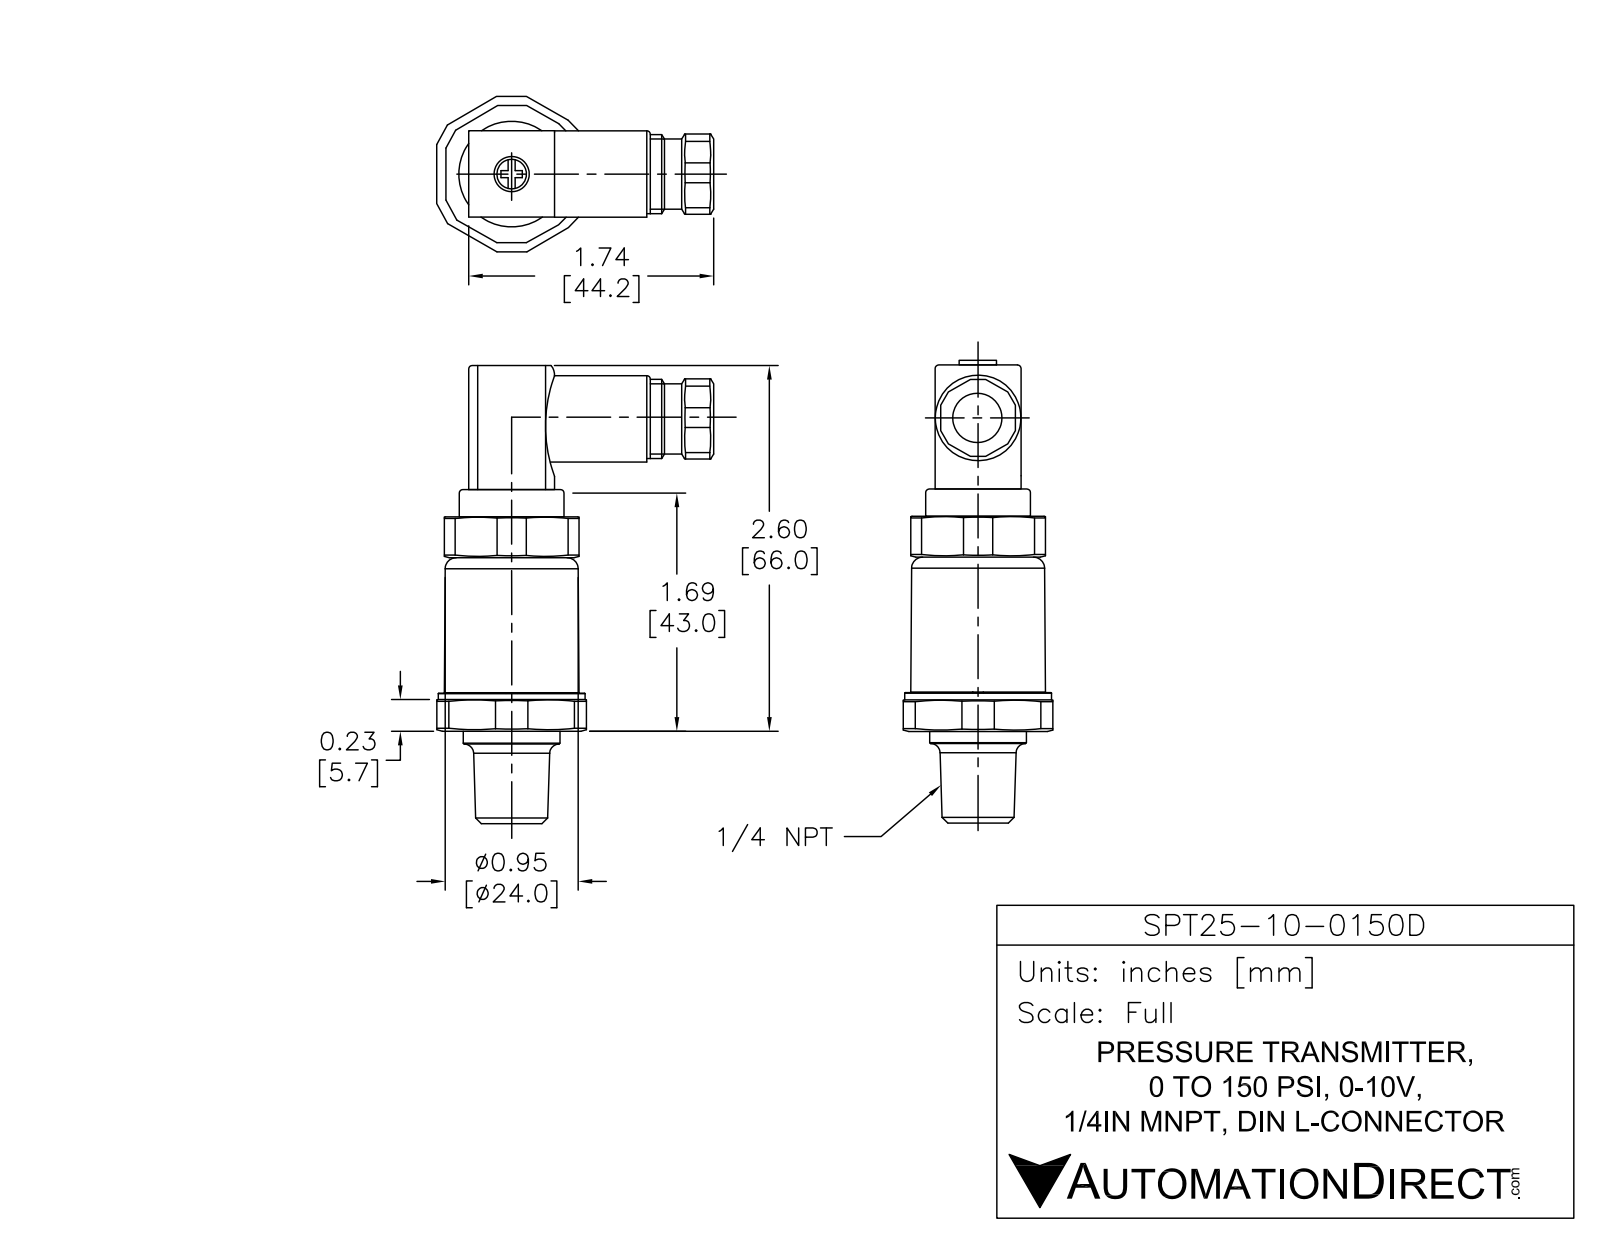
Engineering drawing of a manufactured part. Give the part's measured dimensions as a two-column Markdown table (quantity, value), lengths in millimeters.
| quantity | value |
| --- | --- |
| part name | SPT25-10-0150D |
| STEP written by | SolidWorks 2011 (AUTOMOTIVE_DESIGN) |
| units | millimeters |
| bodies | 5 solids, 170 faces (96 planar, 64 cylindrical, 10 other) |
| overall size | 81.25 × 38.01 × 35.71 |
| volume | 27 900 mm³ |
| surface area | 10 134 mm² |
| round holes (diameter × count) | 1 × 1, 3.3 × 1, 7 × 1, 8 × 1 |
| round bosses / shafts (diameter × count) | 26.75 × 1, 24 × 1, 17.5 × 1, 15 × 1, 14 × 1, 11 × 1 |
| partial cylindrical surfaces (radius × count) | 1.5 × 8, 1.15 × 4, 2.25 × 4, 2 × 3, 1.15 × 1, 1.17 × 1, 14.5 × 1 |
| main face-to-face distances | 1.5, 29.5, 31, 15.75, 0.35, 15.4, 6.75, 37.75, 36.25, 5 |
| hole center spacings | 1.33 |
